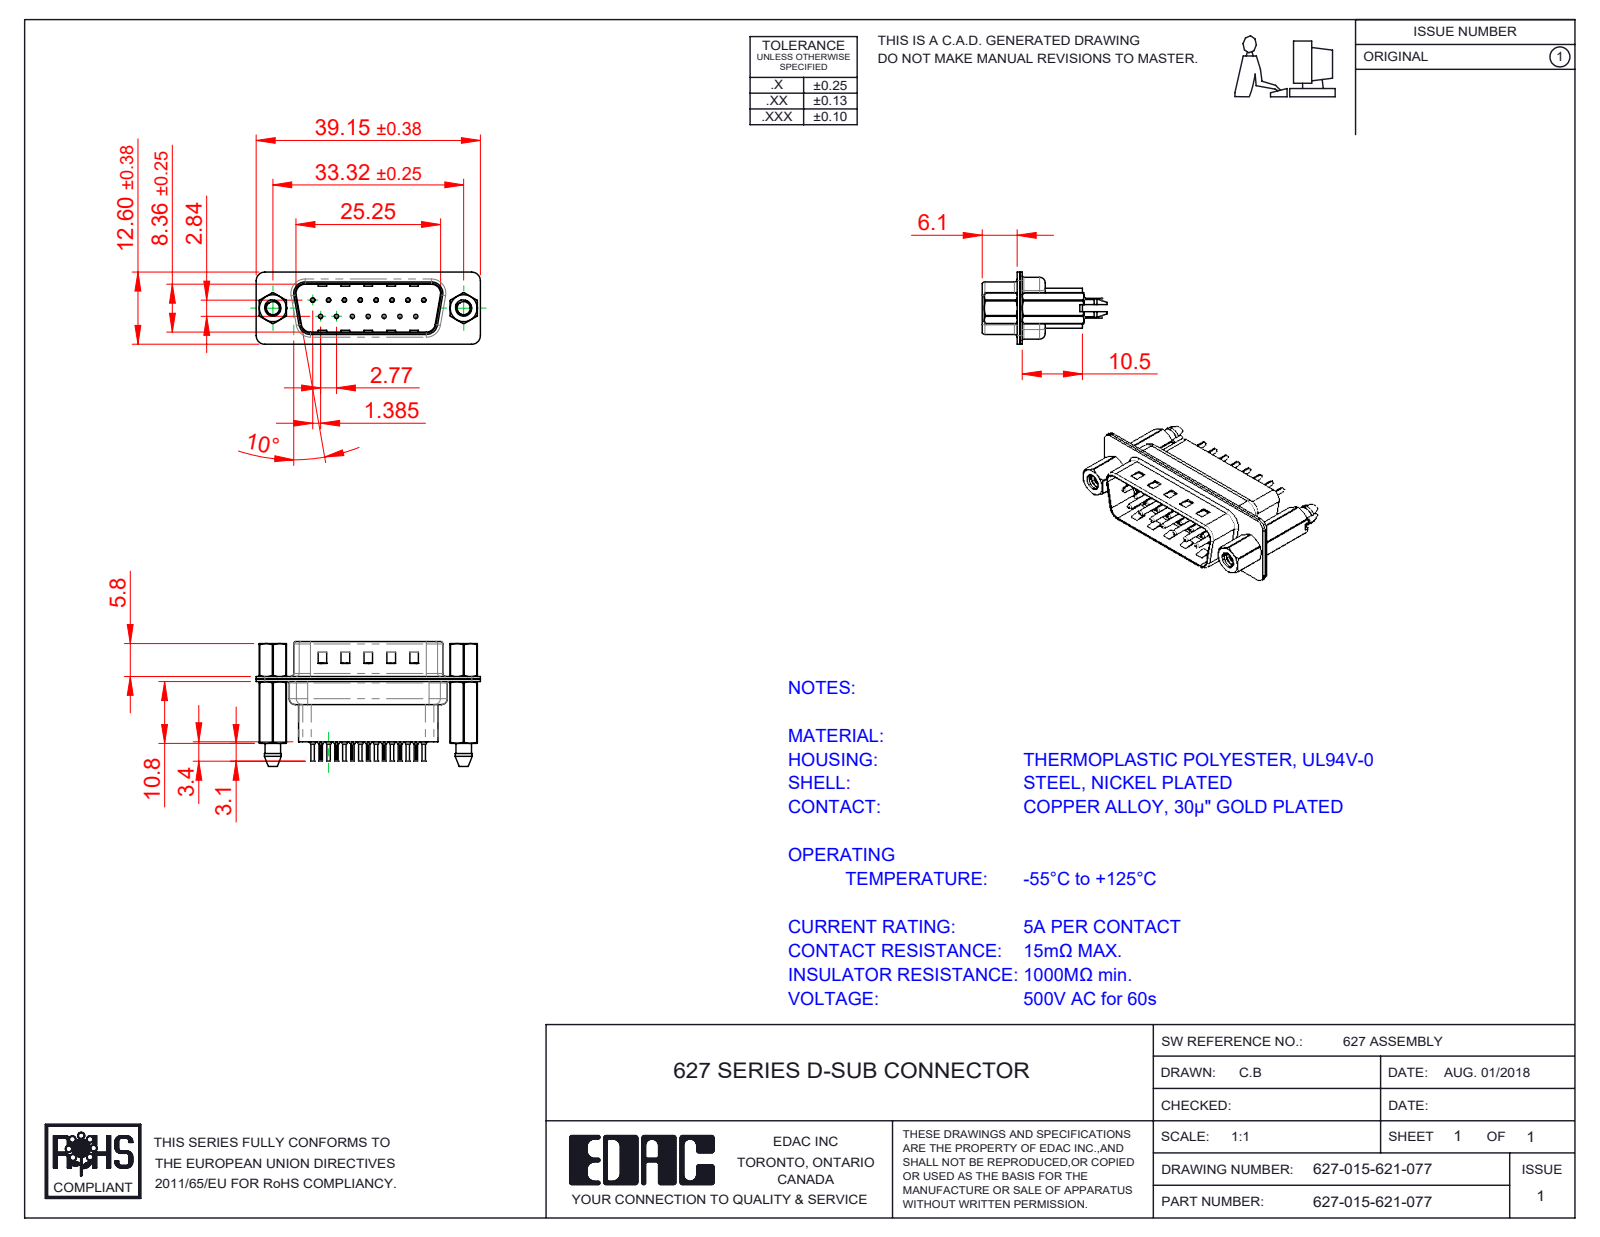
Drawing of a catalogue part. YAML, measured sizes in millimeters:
part_name: "627 Contact Row 1_21H; 627 Shell Rear_15 Contacts; 627 4-40 Threaded Boardlock_HP; 627 4-40 Hex Standoff (+4 more)"
step_written_by: "SolidWorks 2020 (CONFIG_CONTROL_DESIGN)"
units: millimeters
bodies: {solids: 22, faces: 2050, planar: 553, cylindrical: 828, other: 669}
overall_size: [39.15, 21.7, 12.6]
volume: 3002
surface_area: 7676
round_holes:
  - {diameter: 0.2, count: 15}
  - {diameter: 0.35, count: 15}
  - {diameter: 1.1, count: 15}
  - {diameter: 1.6, count: 15}
  - {diameter: 2.26, count: 2}
  - {diameter: 2.29, count: 2}
  - {diameter: 4, count: 2}
  - {diameter: 4.8, count: 2}
round_bosses_or_shafts:
  - {diameter: 2, count: 15}
  - {diameter: 1.5, count: 15}
  - {diameter: 0.75, count: 15}
  - {diameter: 0.6, count: 15}
  - {diameter: 4.9, count: 2}
  - {diameter: 2.79, count: 2}
partial_cylinders:
  - {radius: 0.1, count: 30}
  - {radius: 1.5, count: 18}
  - {radius: 2, count: 12}
  - {radius: 1.6, count: 10}
  - {radius: 0.5, count: 8}
  - {radius: 0.25, count: 4}
  - {radius: 0.6, count: 4}
  - {radius: 0.65, count: 4}
face_to_face_distances: [0.4, 0.45, 0.9, 0.82, 9.58, 4.76, 1.5, 0.68, 7.68, 1.4]
hole_center_spacings: [3.16, 2.77, 5.54, 8.31, 11.08, 5.03, 5.04, 7.48]
